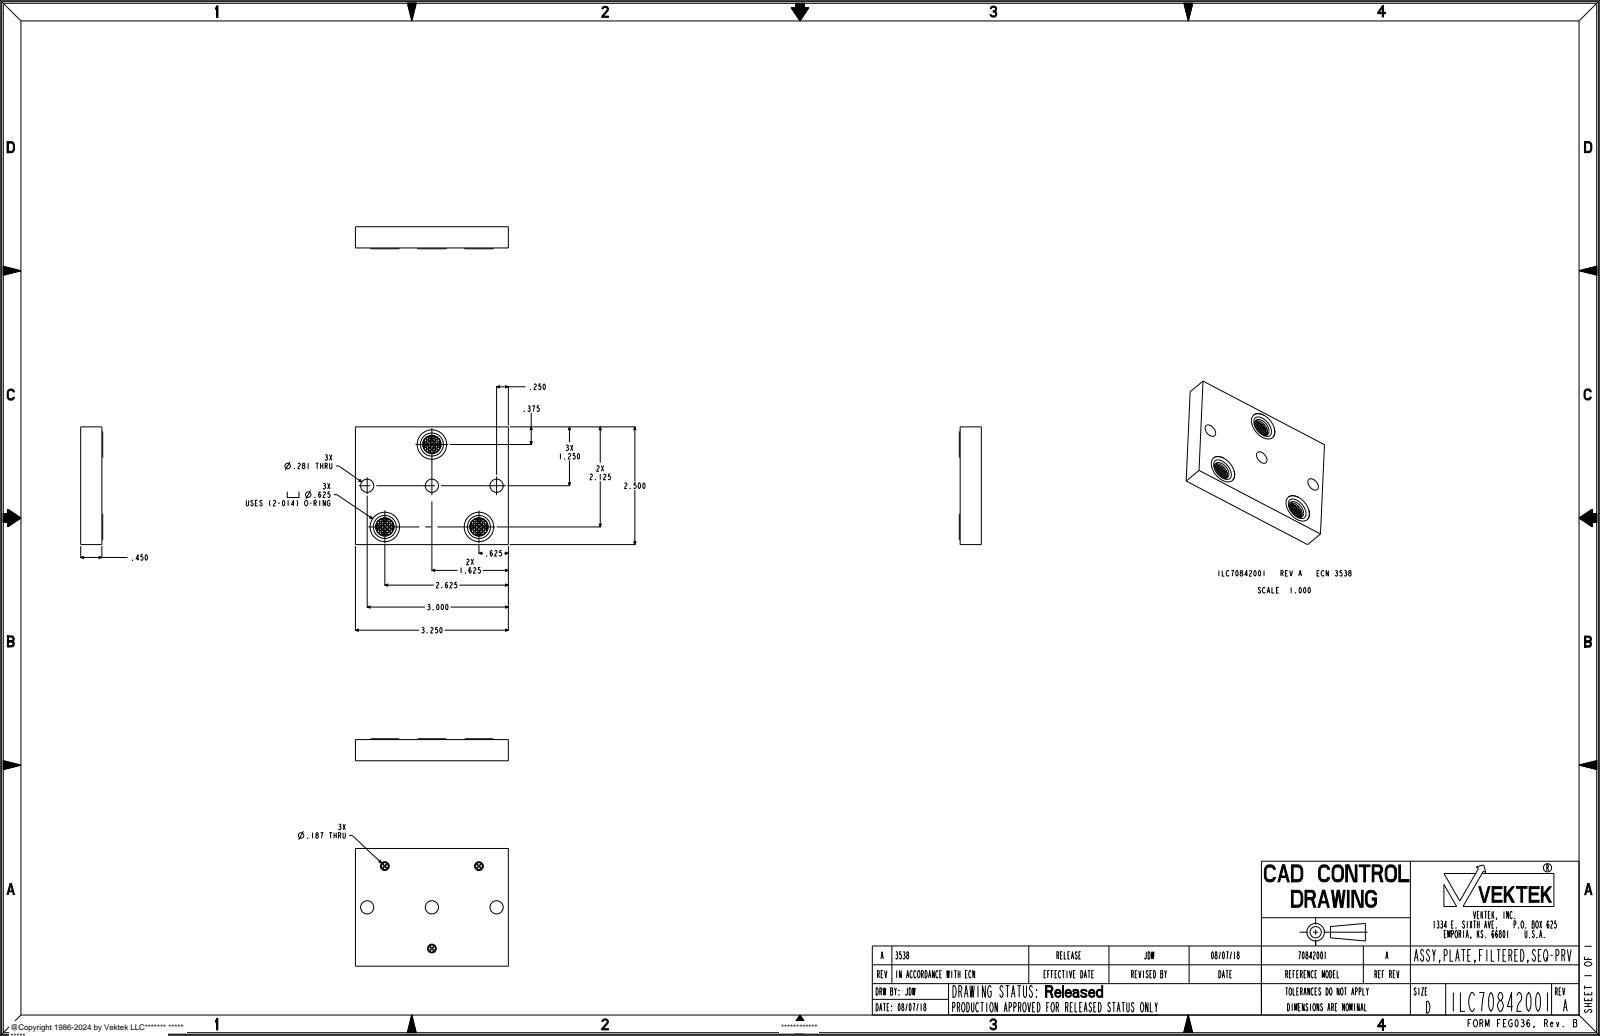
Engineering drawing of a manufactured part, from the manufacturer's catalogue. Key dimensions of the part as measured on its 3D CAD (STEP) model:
Part name (STEP PRODUCT): ILC70842001
STEP written by: PRO/ENGINEER BY PARAMETRIC TECHNOLOGY CORPORATION, 2013320 (AUTOMOTIVE_DESIGN)
Units: inches
Bodies: 1 solid, 693 faces (222 planar, 459 cylindrical, 12 other)
Overall size (bounding box): 3.25 × 2.5 × 0.468
Volume: 3.436 in³ · Surface area: 26.51 in²
Round holes (diameter × count): ⌀0.062 ×48, ⌀0.187 ×3, ⌀0.265 ×3, ⌀0.281 ×3, ⌀0.392 ×3, ⌀0.411 ×3, ⌀0.625 ×3
Round bosses / shafts (diameter × count): ⌀0.371 ×3
Partial cylindrical surfaces — rounded edges, fillets, slot ends (radius × count): R0.031 ×48, R0.01 ×6, R0.015 ×6, R0.023 ×6, R0.187 ×3, R0.19 ×3
Main face-to-face distances: 0.45, 2.5, 3.25, 0.398, 0.052, 0.196, 0.031, 0.082, 0.316, 0.368
Hole centre spacings: 0.094, 0.21, 0.148, 0.133, 0.067, 0.24, 0.133, 0.149
